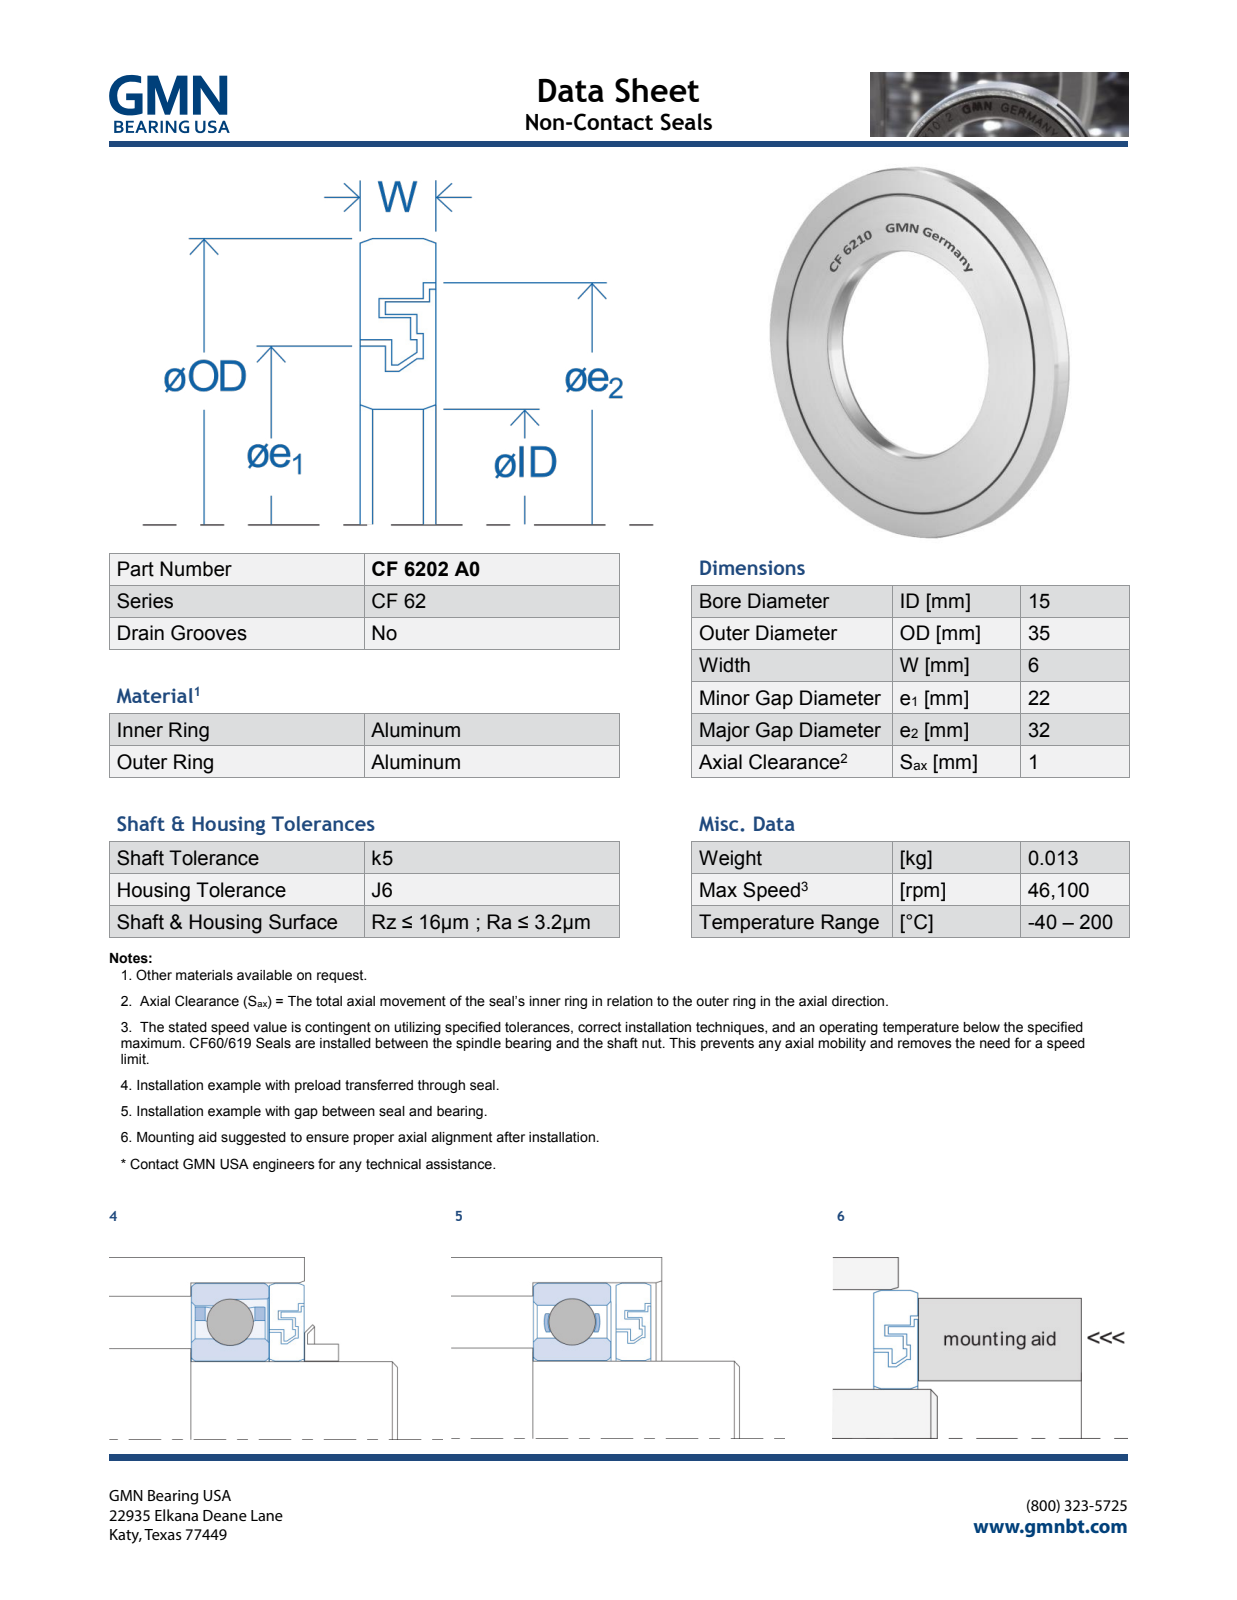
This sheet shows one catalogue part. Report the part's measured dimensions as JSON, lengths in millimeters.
{"part_name": "CF6202A0_PRT", "step_written_by": "PRO/ENGINEER BY PARAMETRIC TECHNOLOGY CORPORATION, 2013150 (AUTOMOTIVE_DESIGN)", "units": "millimeters", "bodies": {"solids": 2, "faces": 607, "planar": 565, "cylindrical": 30, "other": 12}, "overall_size": [35, 35, 6.05], "volume_mm3": 4024, "surface_area_mm2": 5446, "round_holes": [[15, 1], [19, 1], [23, 1], [24, 1], [27, 1], [29.5, 1], [32, 1]], "round_bosses_or_shafts": [[35, 1], [31, 1], [29, 1], [26.5, 1], [22, 1], [20, 1], [18, 1]], "face_to_face_distances": [0.5, 6, 1, 2, 2.5, 1.5, 4, 3, 3.5, 4.5]}
